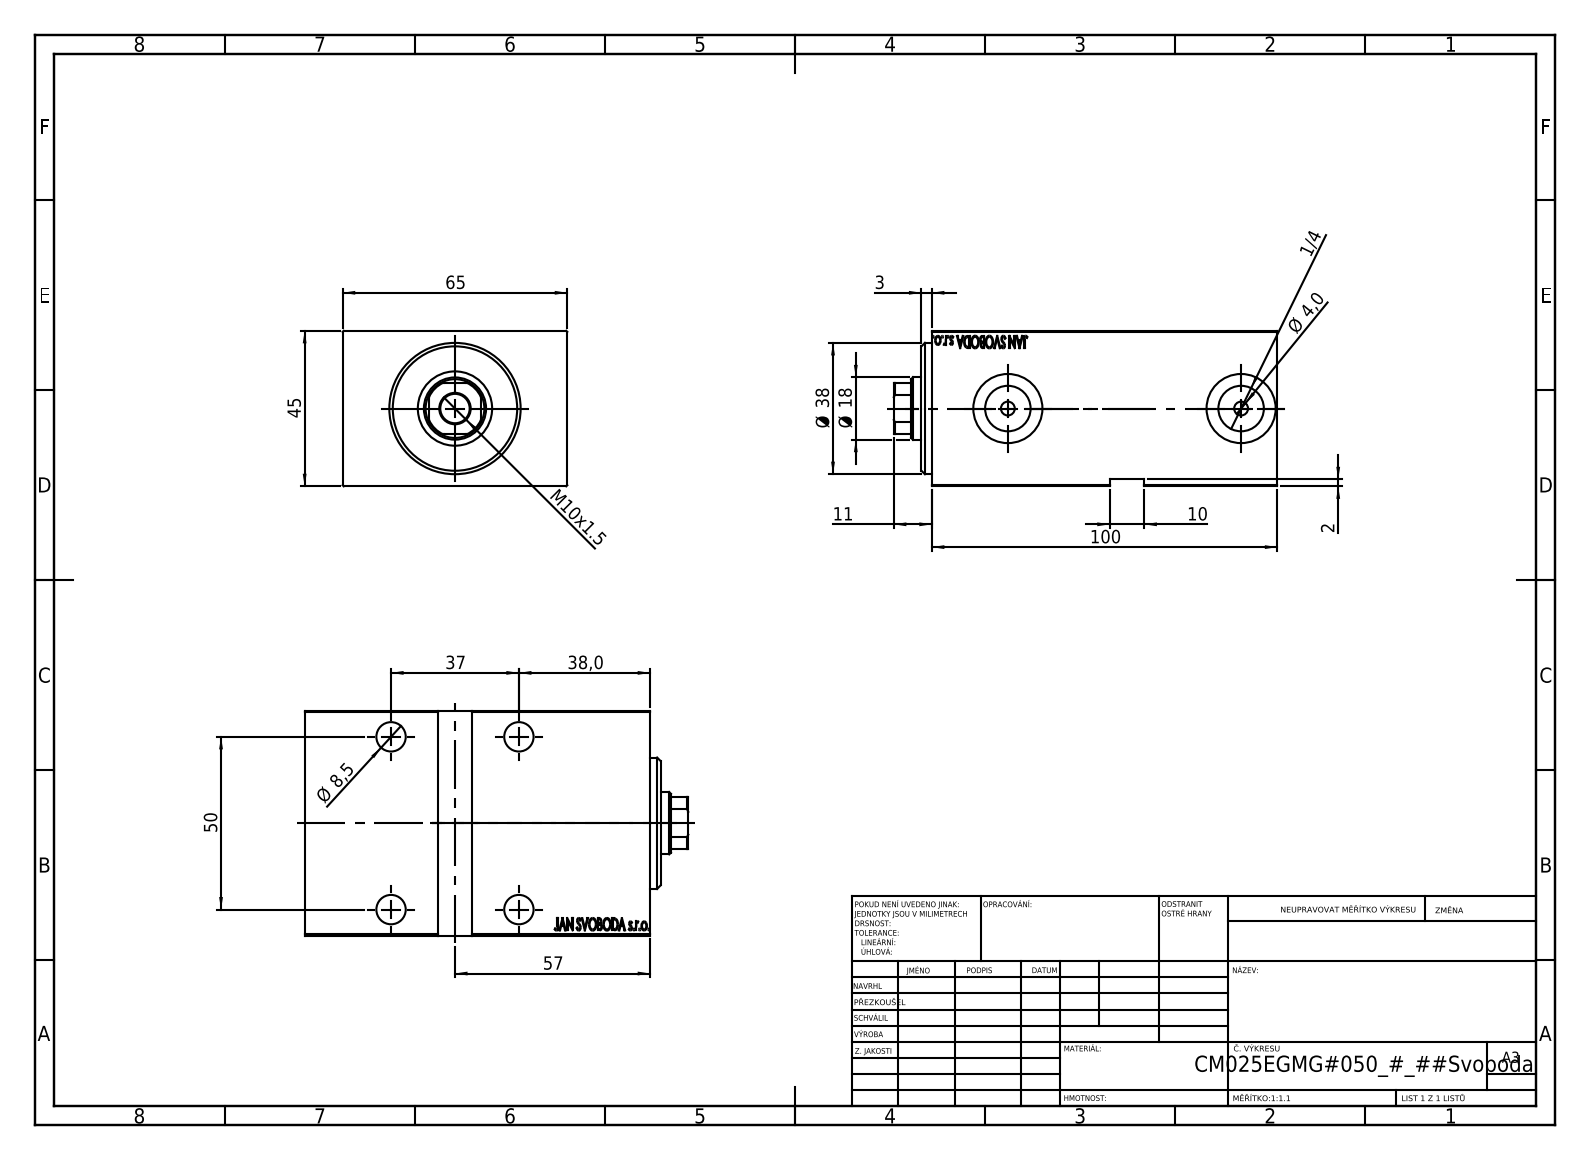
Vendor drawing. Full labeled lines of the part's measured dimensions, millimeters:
Part name (STEP PRODUCT): V450CM_E_VCP; V450CM_VC_B; V450CM_E_Body
STEP written by: SolidWorks 2019 (CONFIG_CONTROL_DESIGN)
Units: millimetres
Bodies: 3 solids, 856 faces (410 planar, 52 cylindrical, 394 other)
Overall size (bounding box): 111 × 65 × 45
Volume: 267 514 mm³ · Surface area: 54 649 mm²
Round holes (diameter × count): ⌀8.5 ×5, ⌀13.5 ×4, ⌀4 ×2, ⌀13.16 ×2, ⌀20 ×2, ⌀18 ×1, ⌀21.5 ×1, ⌀25 ×1, ⌀35 ×1
Round bosses / shafts (diameter × count): ⌀38 ×1, ⌀27 ×1
Partial cylindrical surfaces — rounded edges, fillets, slot ends (radius × count): R8.5 ×1
Main face-to-face distances: 45, 65, 100, 6, 94, 5, 95, 89, 8, 3
Hole centre spacings: 37, 50, 62.2, 67.5
